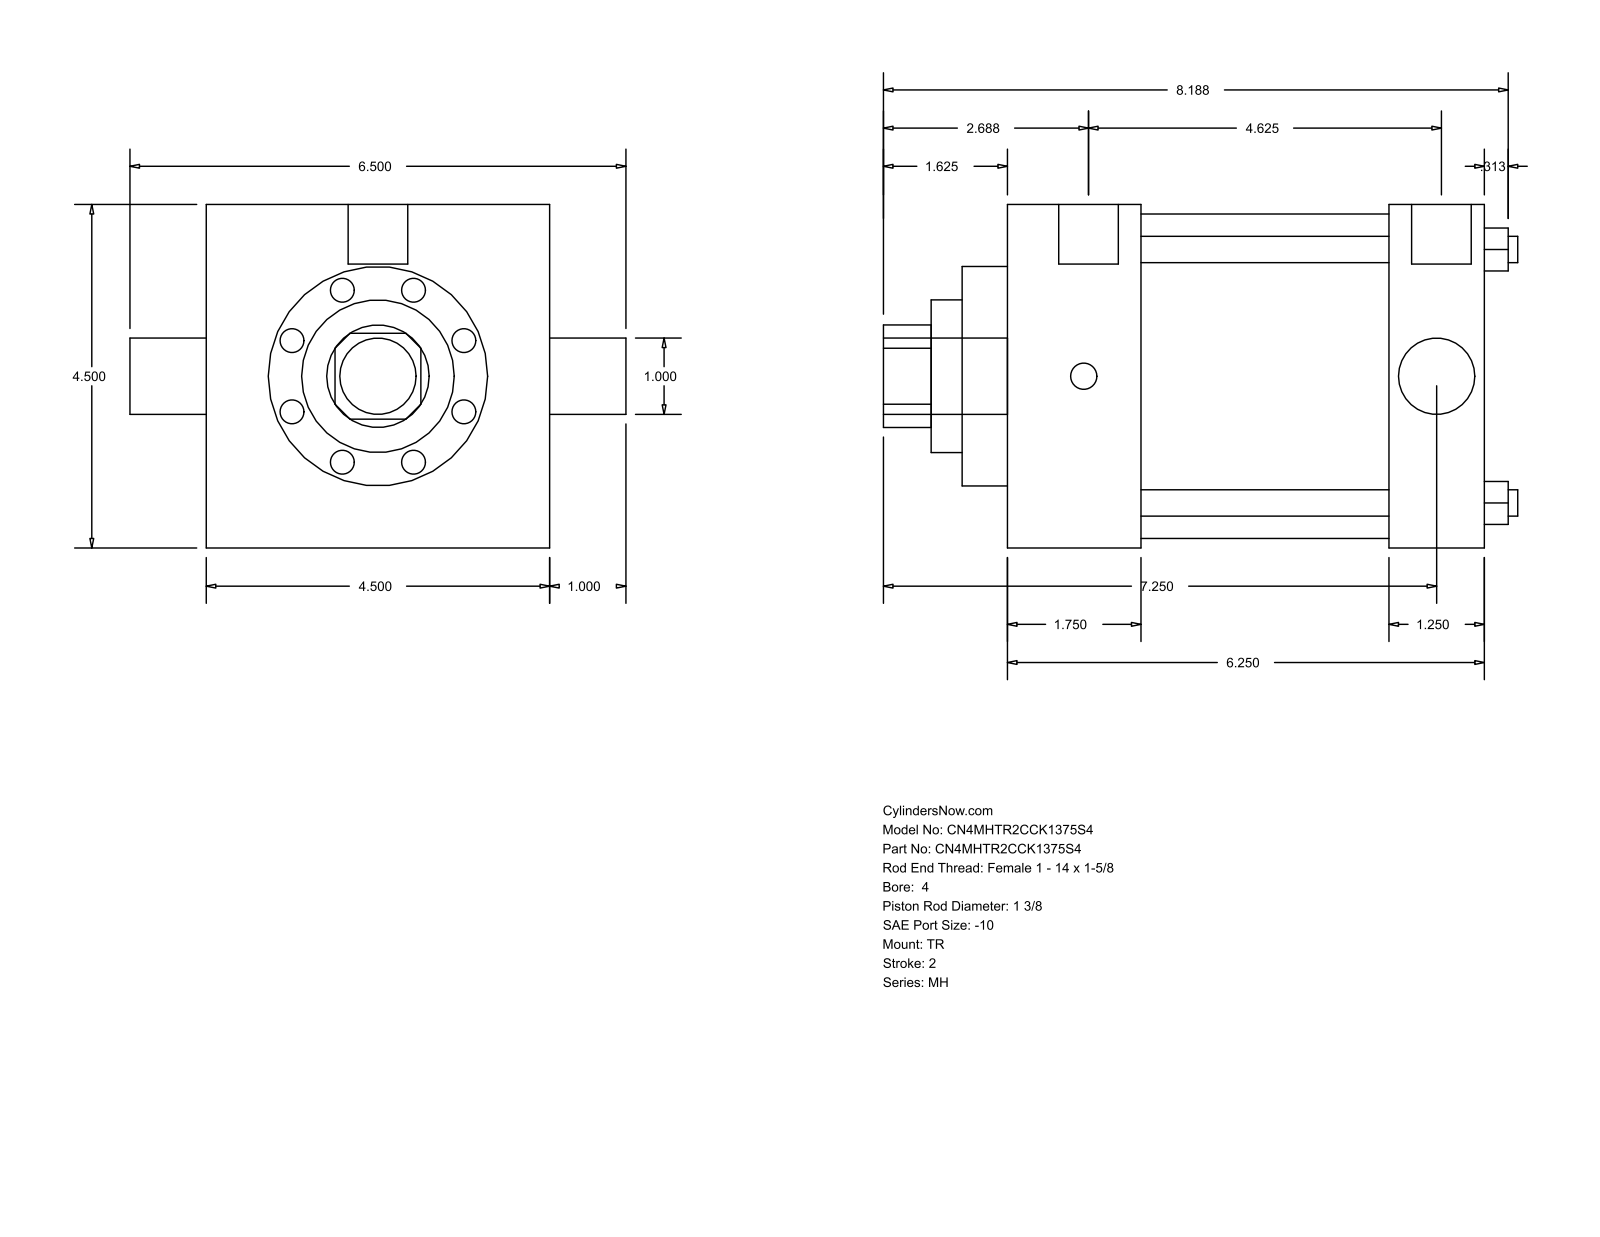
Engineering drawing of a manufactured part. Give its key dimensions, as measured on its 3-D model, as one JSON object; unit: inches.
{"part_name": "MH_TR__0400_1.375", "step_written_by": "GSSL Pune (CONFIG_CONTROL_DESIGN)", "units": "inches", "bodies": {"solids": 0, "faces": 86, "planar": 61, "cylindrical": 25, "other": 0}, "overall_size": [8.313, 6.5, 4.5], "round_holes": [[0.345, 4], [1, 1], [1.375, 1], [2, 1], [2.875, 1], [4.25, 1]], "round_bosses_or_shafts": [[0.344, 3], [0.781, 2], [1, 1]], "partial_cylinders_radius": [[0.672, 1]], "face_to_face_distances": [4.5, 6.25, 1.75, 4.5, 5, 3.25, 1.25, 0.594, 2.344, 5.594], "hole_center_spacings": [2.347, 3.32, 4.695]}
